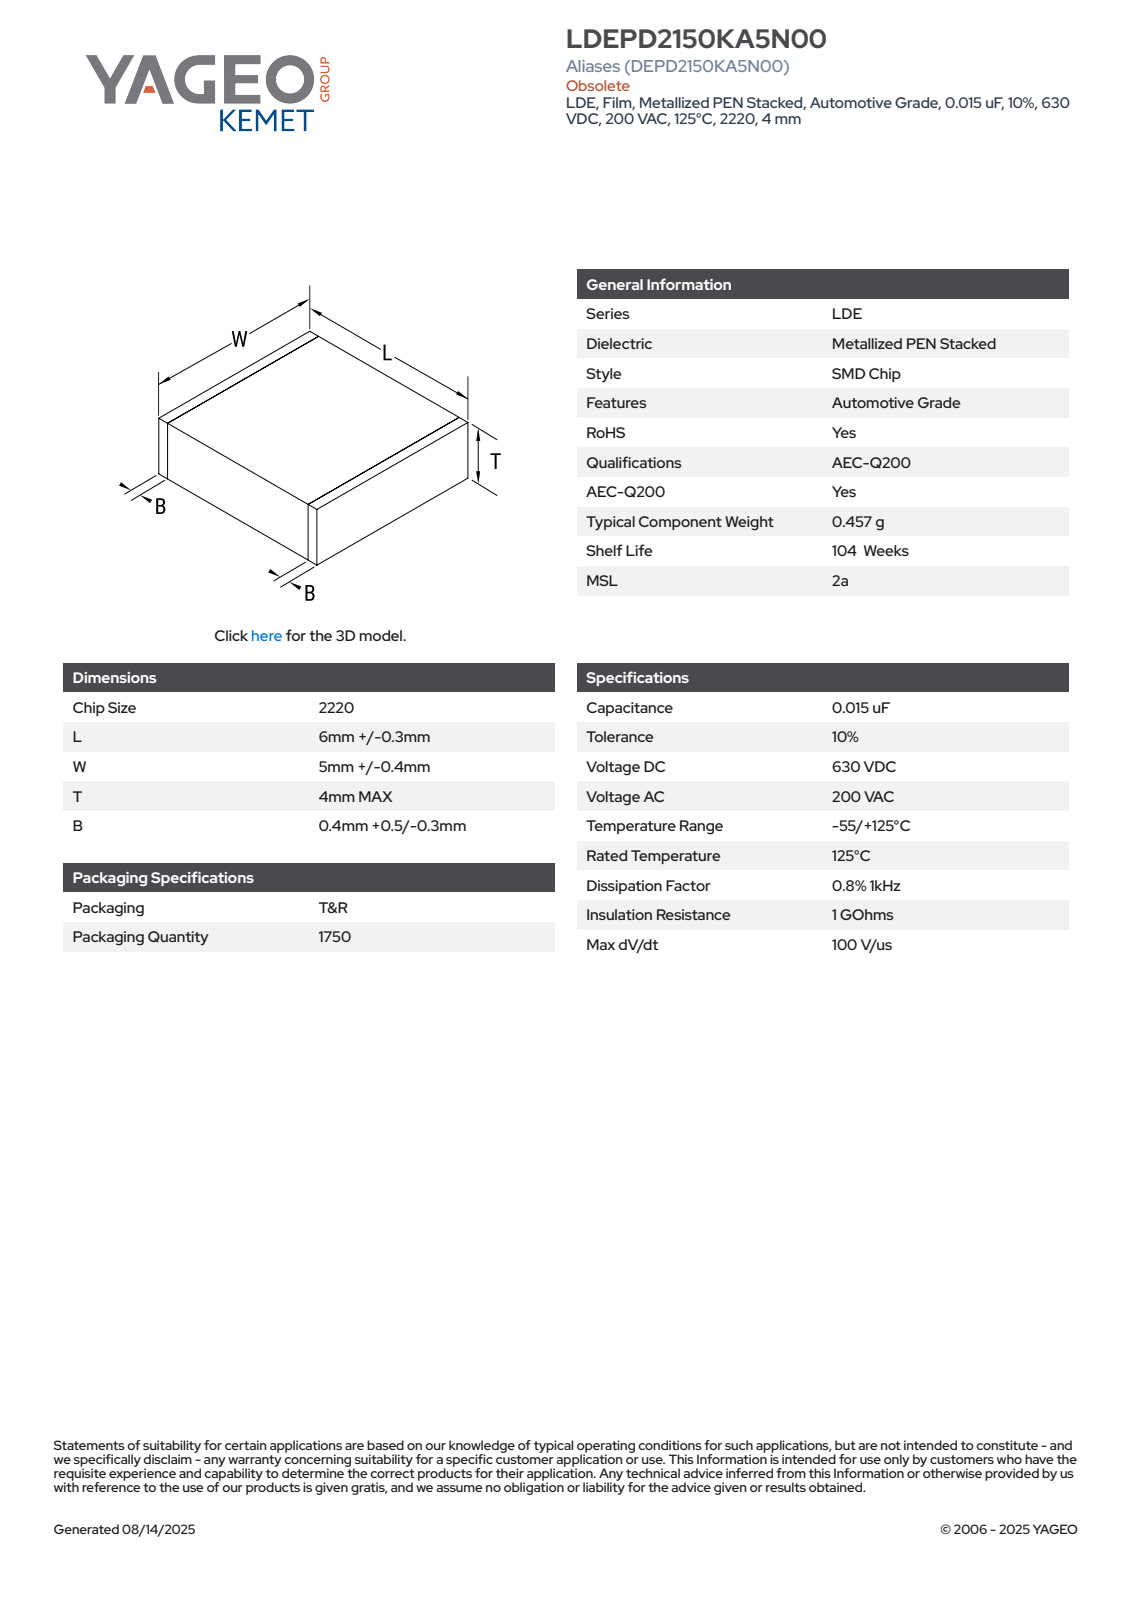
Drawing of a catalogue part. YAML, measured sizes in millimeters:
part_name: "CFS_LDELDB_2220_L6.3W5.4T4B0.9"
step_written_by: "SolidWorks 2020 (AUTOMOTIVE_DESIGN)"
units: millimeters
bodies: {solids: 4, faces: 73, planar: 73, cylindrical: 0, other: 0}
overall_size: [6.3, 5.4, 4]
volume: 135
surface_area: 164
face_to_face_distances: [3.98, 6.3, 5.38, 3.99, 5.39, 4, 5.4, 0.5, 5.8, 5.3]
